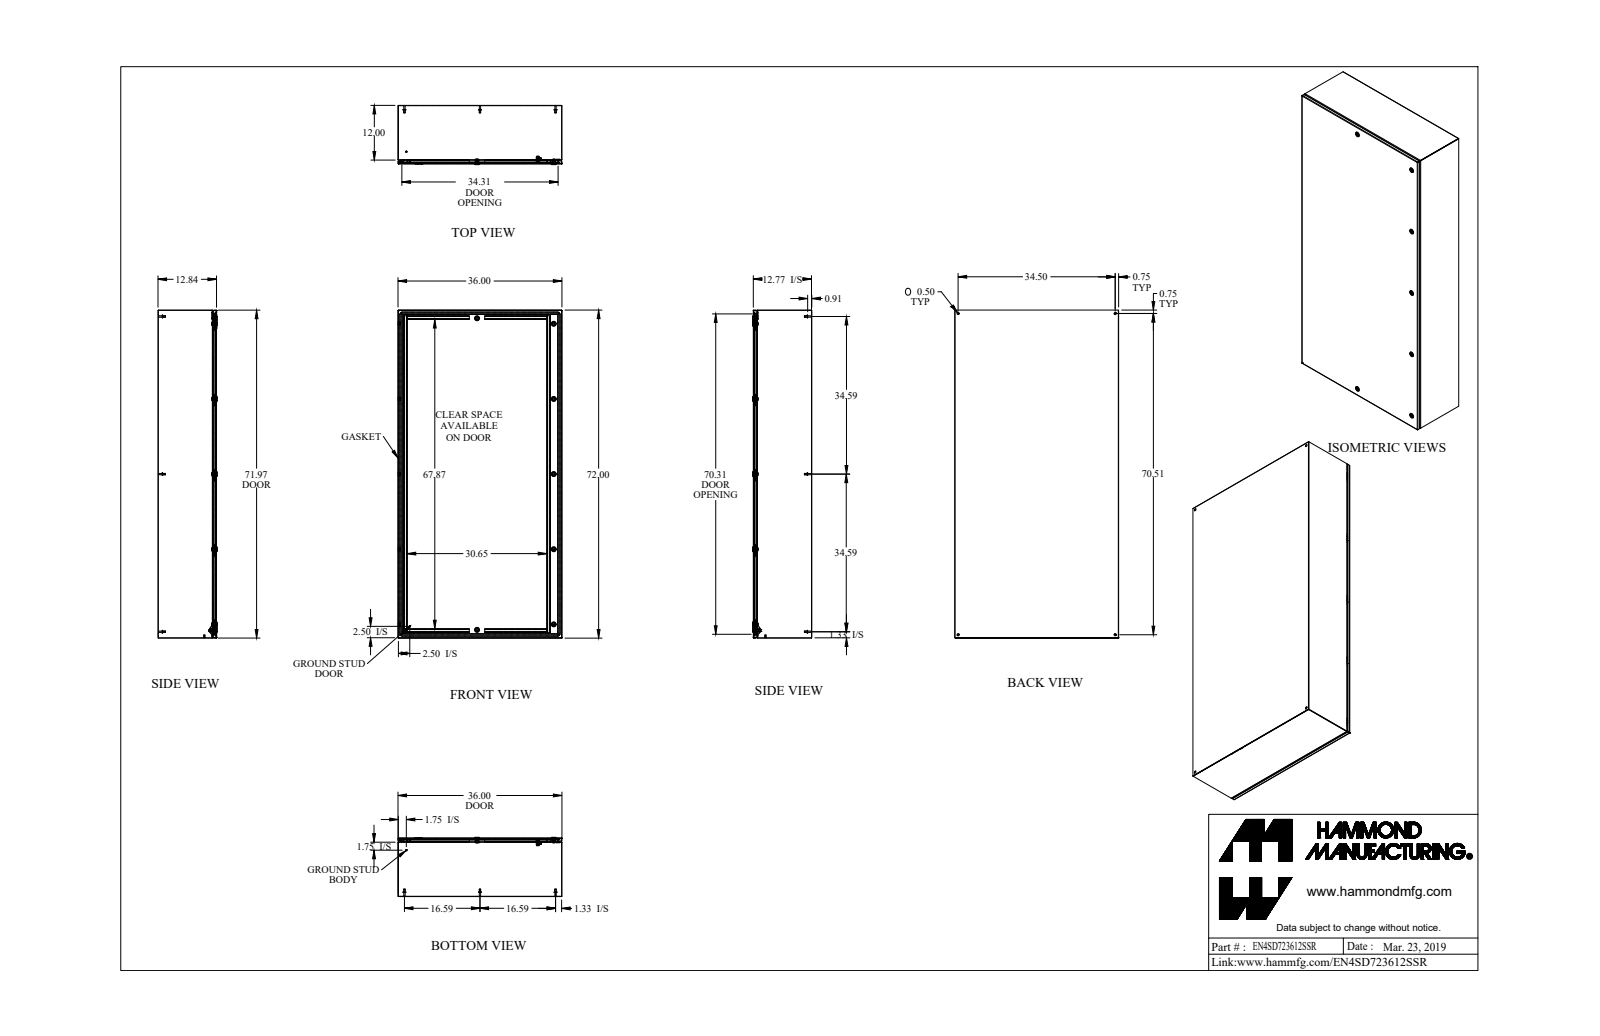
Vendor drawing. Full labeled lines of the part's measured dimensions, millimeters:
Part name (STEP PRODUCT): EN4SD723612SSR
STEP written by: SolidWorks 2018 (AUTOMOTIVE_DESIGN)
Units: millimetres
Bodies: 81 solids, 2027 faces (1092 planar, 634 cylindrical, 301 other)
Overall size (bounding box): 1828.8 × 914.4 × 330.3
Volume: 10 450 000 mm³ · Surface area: 11 680 000 mm²
Round holes (diameter × count): ⌀12.7 ×11, ⌀5 ×7, ⌀9.8 ×7, ⌀16 ×7, ⌀19.5 ×7, ⌀4.4 ×1, ⌀5 ×1, ⌀6.1 ×1, ⌀6.1 ×1, ⌀7 ×1, ⌀9.5 ×1
Round bosses / shafts (diameter × count): ⌀15.9 ×11, ⌀8 ×10, ⌀7 ×8, ⌀27.9 ×7, ⌀6 ×7, ⌀19.9 ×5, ⌀15.9 ×5, ⌀13.3 ×5
Partial cylindrical surfaces — rounded edges, fillets, slot ends (radius × count): R1.1 ×24, R1.6 ×19, R0.9 ×17, R2.7 ×17, R3.2 ×14, R0.2 ×10, R2.4 ×10, R0.4 ×9
Main face-to-face distances: 1.8, 324.4, 322.5, 326.2, 912.6, 910.7, 914.4, 1.8, 1825.1, 1827
Hole centre spacings: 418.9, 837.8, 422.5, 428.8, 455.4, 620.5, 876.3, 968
